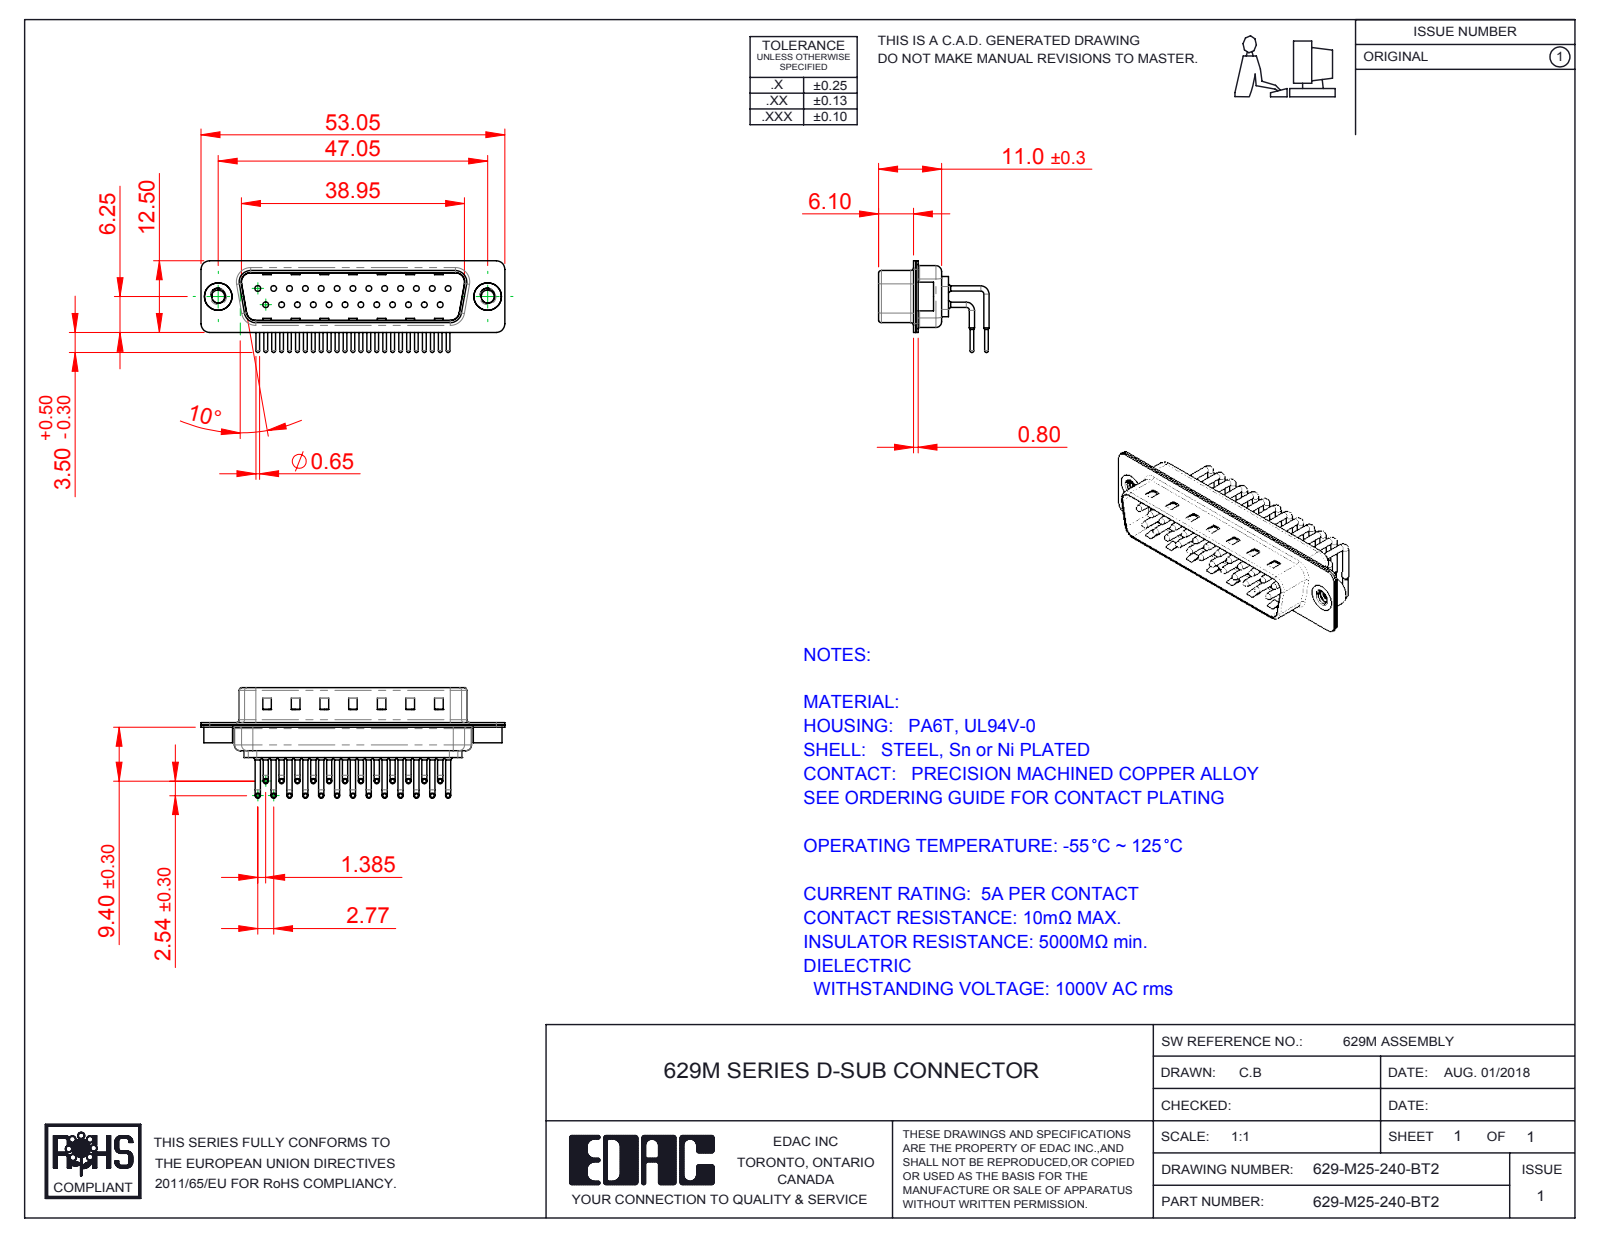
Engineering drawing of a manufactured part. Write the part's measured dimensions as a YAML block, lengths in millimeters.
part_name: "629-M25-240-BT2; 629M Housing_25 Contacts; 629M Contact Row 2; 629M 4-40 Threaded Rivet (+3 more)"
step_written_by: "SolidWorks 2016 (CONFIG_CONTROL_DESIGN)"
units: millimeters
bodies: {solids: 30, faces: 3126, planar: 1771, cylindrical: 1037, other: 318}
overall_size: [53.05, 19.29, 16]
volume: 2911
surface_area: 7760
round_holes:
  - {diameter: 1, count: 25}
  - {diameter: 1.7, count: 25}
  - {diameter: 2, count: 25}
  - {diameter: 2.26, count: 2}
  - {diameter: 4, count: 2}
  - {diameter: 4.8, count: 2}
round_bosses_or_shafts:
  - {diameter: 0.9, count: 50}
  - {diameter: 1.5, count: 25}
  - {diameter: 0.65, count: 25}
  - {diameter: 5, count: 2}
  - {diameter: 4.9, count: 2}
partial_cylinders:
  - {radius: 1.01, count: 25}
  - {radius: 1.5, count: 16}
  - {radius: 2, count: 12}
  - {radius: 0.5, count: 8}
  - {radius: 1.6, count: 8}
  - {radius: 0.25, count: 4}
  - {radius: 0.6, count: 4}
  - {radius: 0.65, count: 4}
face_to_face_distances: [0.4, 0.85, 9.55, 8.7, 1.25, 10.4, 1.5, 1.9, 0.35, 6.1]
hole_center_spacings: [3.16, 2.77, 5.54, 8.31, 11.08, 13.85, 5.04, 7.49]
